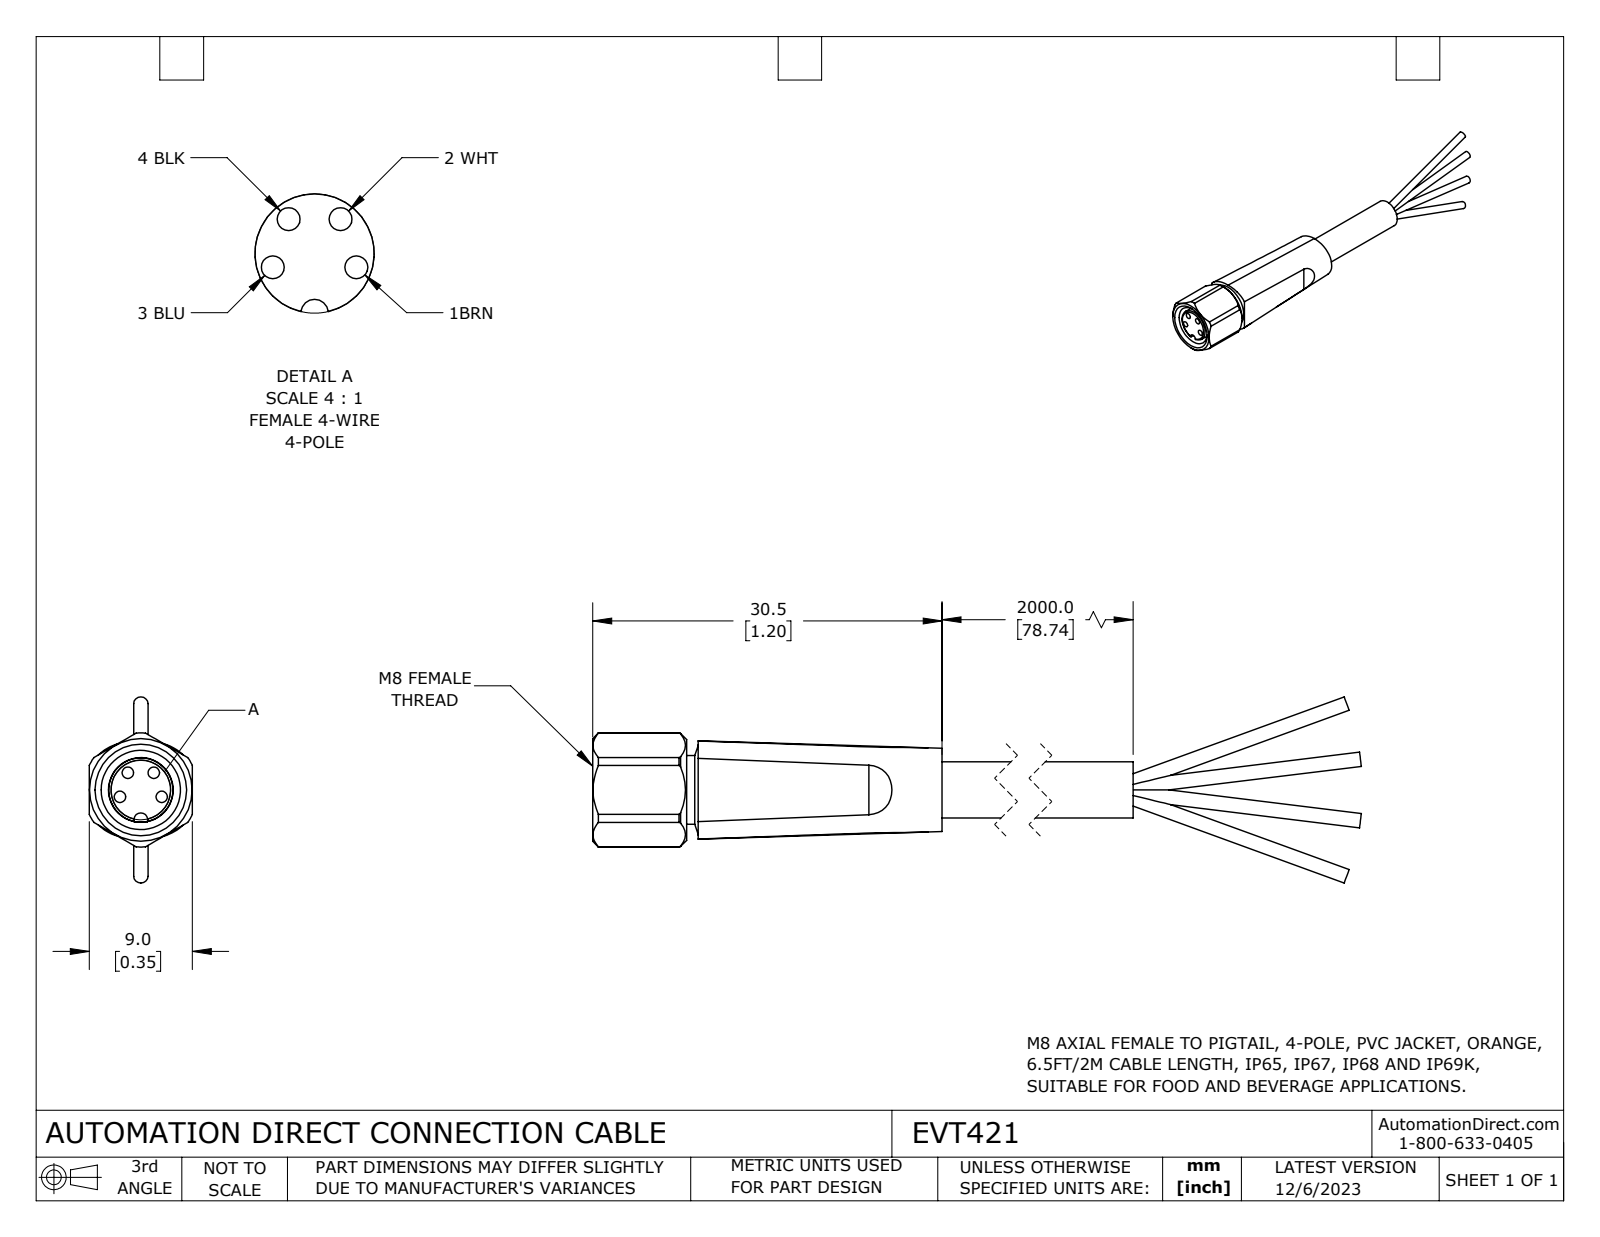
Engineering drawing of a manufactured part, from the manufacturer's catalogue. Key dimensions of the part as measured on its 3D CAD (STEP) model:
Part name (STEP PRODUCT): EVT421
STEP written by: SolidWorks 2023 (CONFIG_CONTROL_DESIGN)
Units: inches
Bodies: 1 solid, 82 faces (26 planar, 35 cylindrical, 21 other)
Overall size (bounding box): 2.694 × 0.64 × 0.354
Volume: 0.126 in³ · Surface area: 3.03 in²
Round holes (diameter × count): ⌀0.039 ×4, ⌀0.272 ×1
Round bosses / shafts (diameter × count): ⌀0.049 ×4, ⌀0.236 ×1, ⌀0.222 ×1, ⌀0.193 ×1
Partial cylindrical surfaces — rounded edges, fillets, slot ends (radius × count): R0.133 ×2, R0.024 ×1, R0.196 ×1
Main face-to-face distances: 0.354, 0.878, 0.303, 1.181, 1.89, 1.587, 0.709, 0.272, 0.031, 0.909
Hole centre spacings: 0.074, 0.076, 0.087, 0.143, 0.089, 0.143
